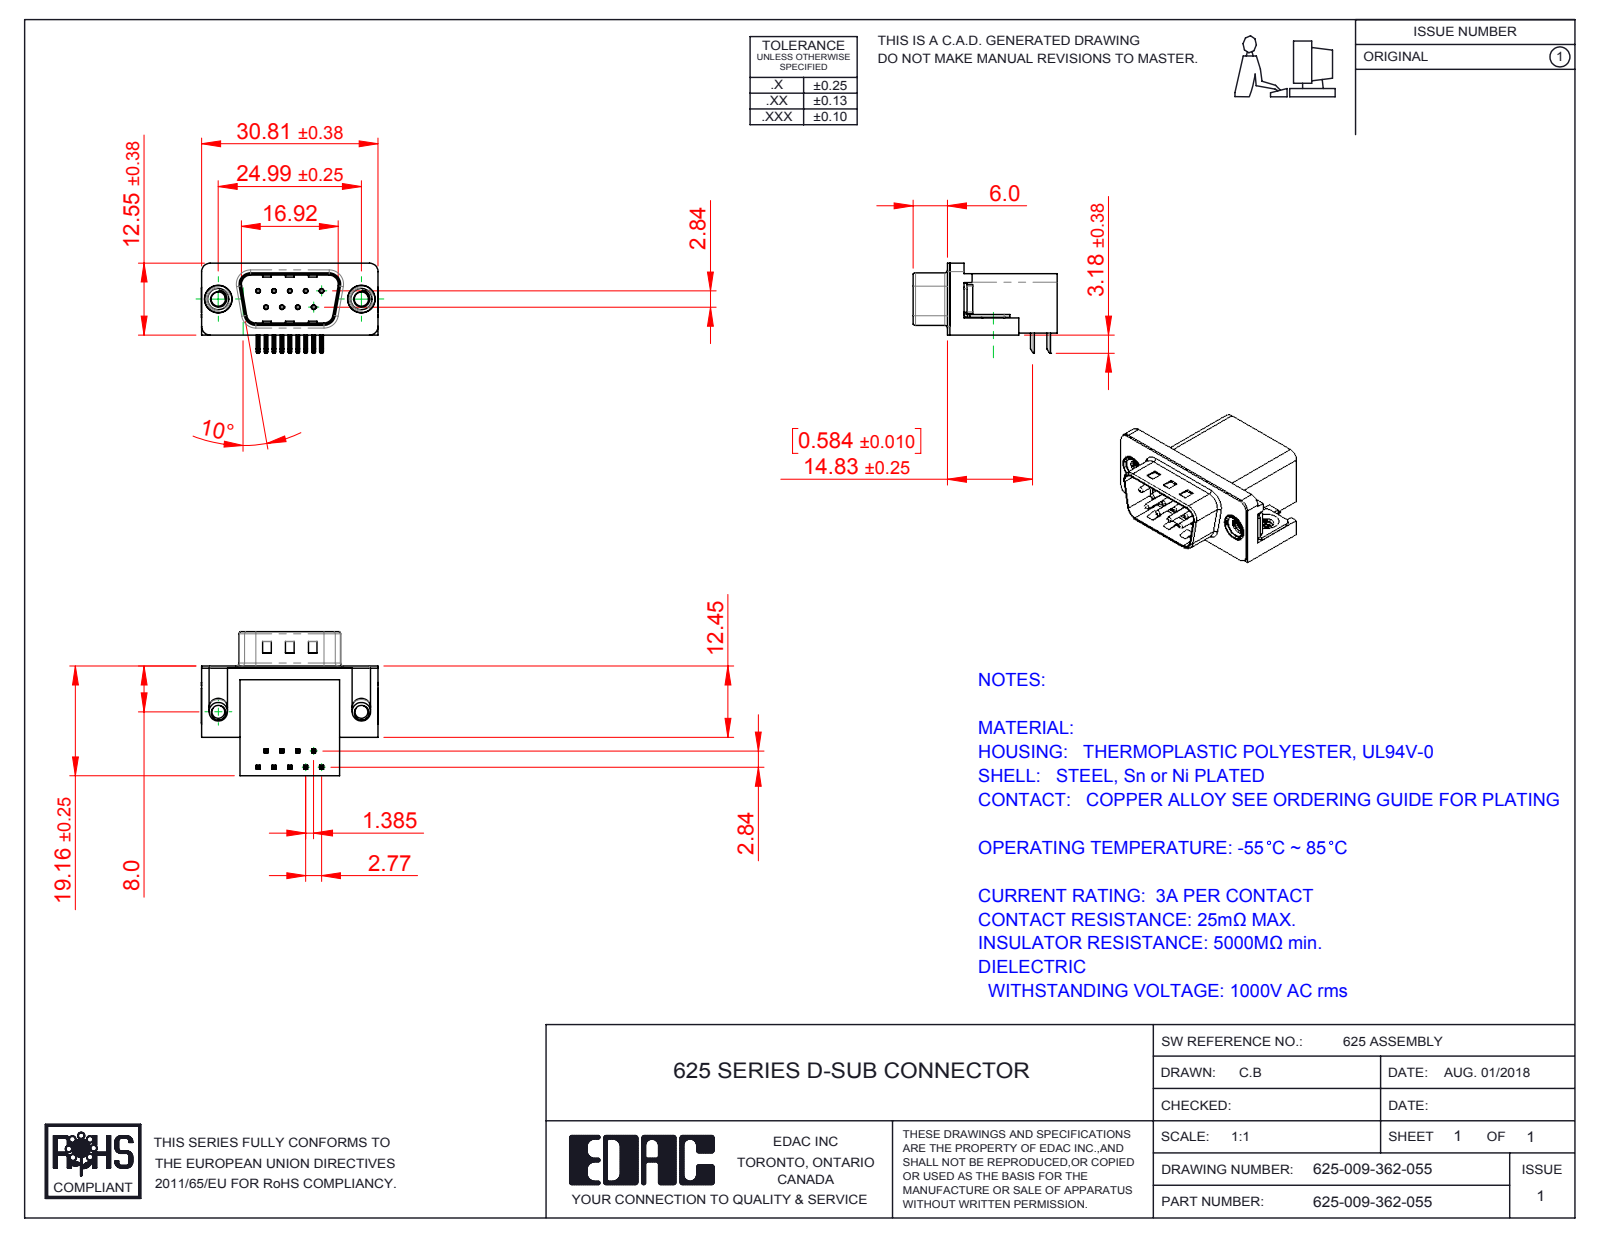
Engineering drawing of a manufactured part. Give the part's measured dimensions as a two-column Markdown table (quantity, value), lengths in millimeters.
| quantity | value |
| --- | --- |
| part name | 625-009-362-055; 625 M3 Threaded Rivet; 625 4-40 Threaded Board Mount; 625 Contact Top (+3 more) |
| STEP written by | SolidWorks 2016 (CONFIG_CONTROL_DESIGN) |
| units | millimeters |
| bodies | 15 solids, 1025 faces (575 planar, 333 cylindrical, 117 other) |
| overall size | 30.89 × 25.16 × 15.73 |
| volume | 4 481 mm³ |
| surface area | 5 034 mm² |
| round holes (diameter × count) | 0.35 × 9, 0.8 × 9, 2.26 × 2, 2.5 × 2, 4 × 2, 4.8 × 2, 5 × 2 |
| round bosses / shafts (diameter × count) | 0.75 × 9, 4.9 × 2, 4.75 × 2, 3.9 × 2, 3.26 × 2 |
| partial cylindrical surfaces (radius × count) | 0.25 × 44, 0.12 × 18, 1 × 16, 0.5 × 9, 1.5 × 8, 1.6 × 8, 0.9 × 4, 2 × 4 |
| main face-to-face distances | 0.4, 10.34, 18.76, 19.16, 2.9, 16.26, 2.5, 0.35, 10.69, 6.7 |
| hole center spacings | 3.16, 2.77, 5.54, 5.03, 5.04, 8.31, 7.48, 7.49 |
